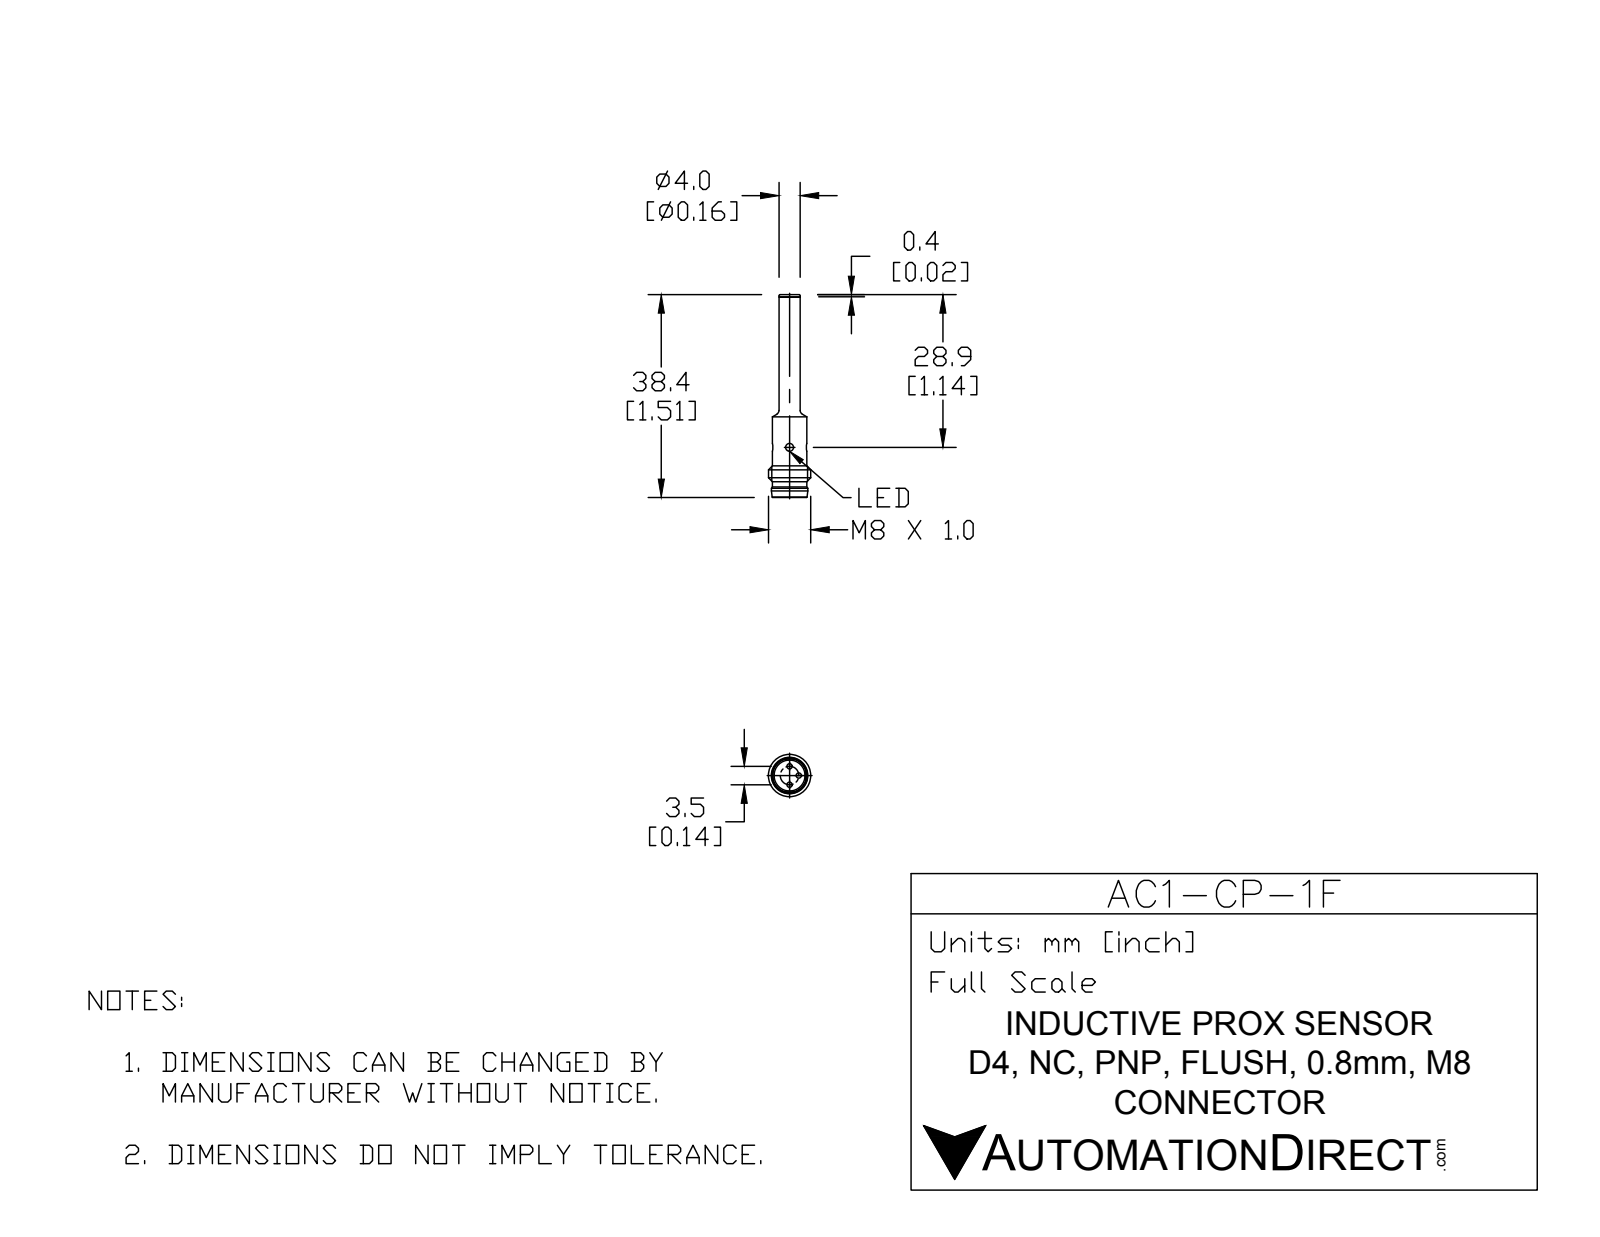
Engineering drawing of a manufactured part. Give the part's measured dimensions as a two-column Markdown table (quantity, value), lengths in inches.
| quantity | value |
| --- | --- |
| part name | AC1-CP-1F |
| STEP written by | SolidWorks 2015 (CONFIG_CONTROL_DESIGN) |
| units | inches |
| bodies | 4 solids, 59 faces (11 planar, 26 cylindrical, 22 other) |
| overall size | 1.512 × 0.315 × 0.315 |
| volume | 0.046 in³ |
| surface area | 1.3 in² |
| round holes (diameter × count) | 0.059 × 2, 0.23 × 1 |
| round bosses / shafts (diameter × count) | 0.039 × 3, 0.315 × 1, 0.272 × 1, 0.256 × 1, 0.157 × 1 |
| main face-to-face distances | 1.315, 0.217, 0.197, 1.512, 1.496, 1.299, 0.016 |
